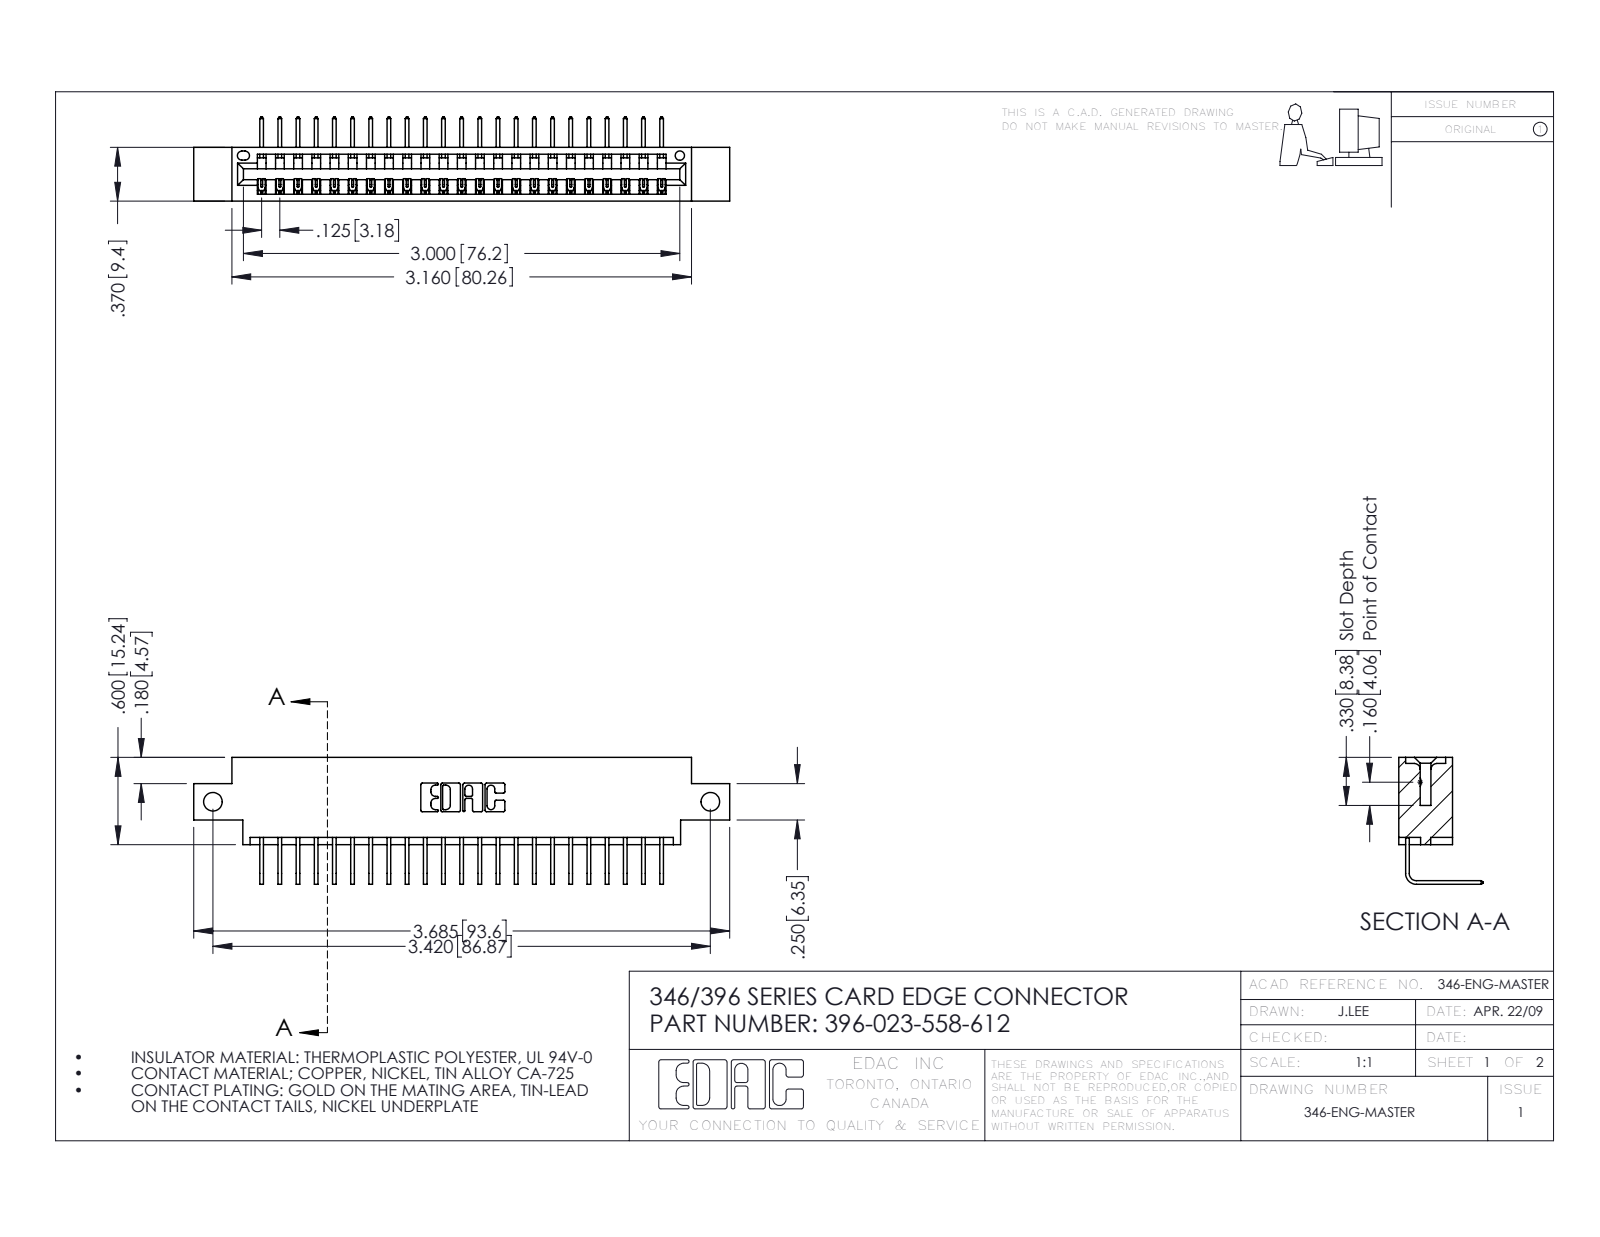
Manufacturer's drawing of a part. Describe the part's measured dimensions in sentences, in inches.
The part is named "396-023-558-612; 345-292-001_558 Tail - 2; 346 Part_0.170 Offset - Side Mount". Its 3-D file was written by "SolidWorks 2016 (CONFIG_CONTROL_DESIGN)". It is 24 solids with 1506 faces: 1046 planar, 460 cylindrical and 0 other. Overall it measures 3.685 by 0.873 by 0.58 inches. Its volume is 0.529 cubic inches and its surface area 17.2 square inches. Round holes: 2 of diameter 0.128, 1 of diameter 0.064. Partial cylindrical surfaces (rounded edges, fillets, slot ends): 46 of radius 0.006, 22 of radius 0.01, 6 of radius 0.007, 6 of radius 0.031, 3 of radius 0.026, 2 of radius 0.031, 2 of radius 0.04, 1 of radius 0.014. The main face-to-face distances are 0.322, 0.048, 0.37, 0.25, 0.298, 0.025, 0.072, 0.148, 0.222, 0.1. The hole center spacings are 3.42.
